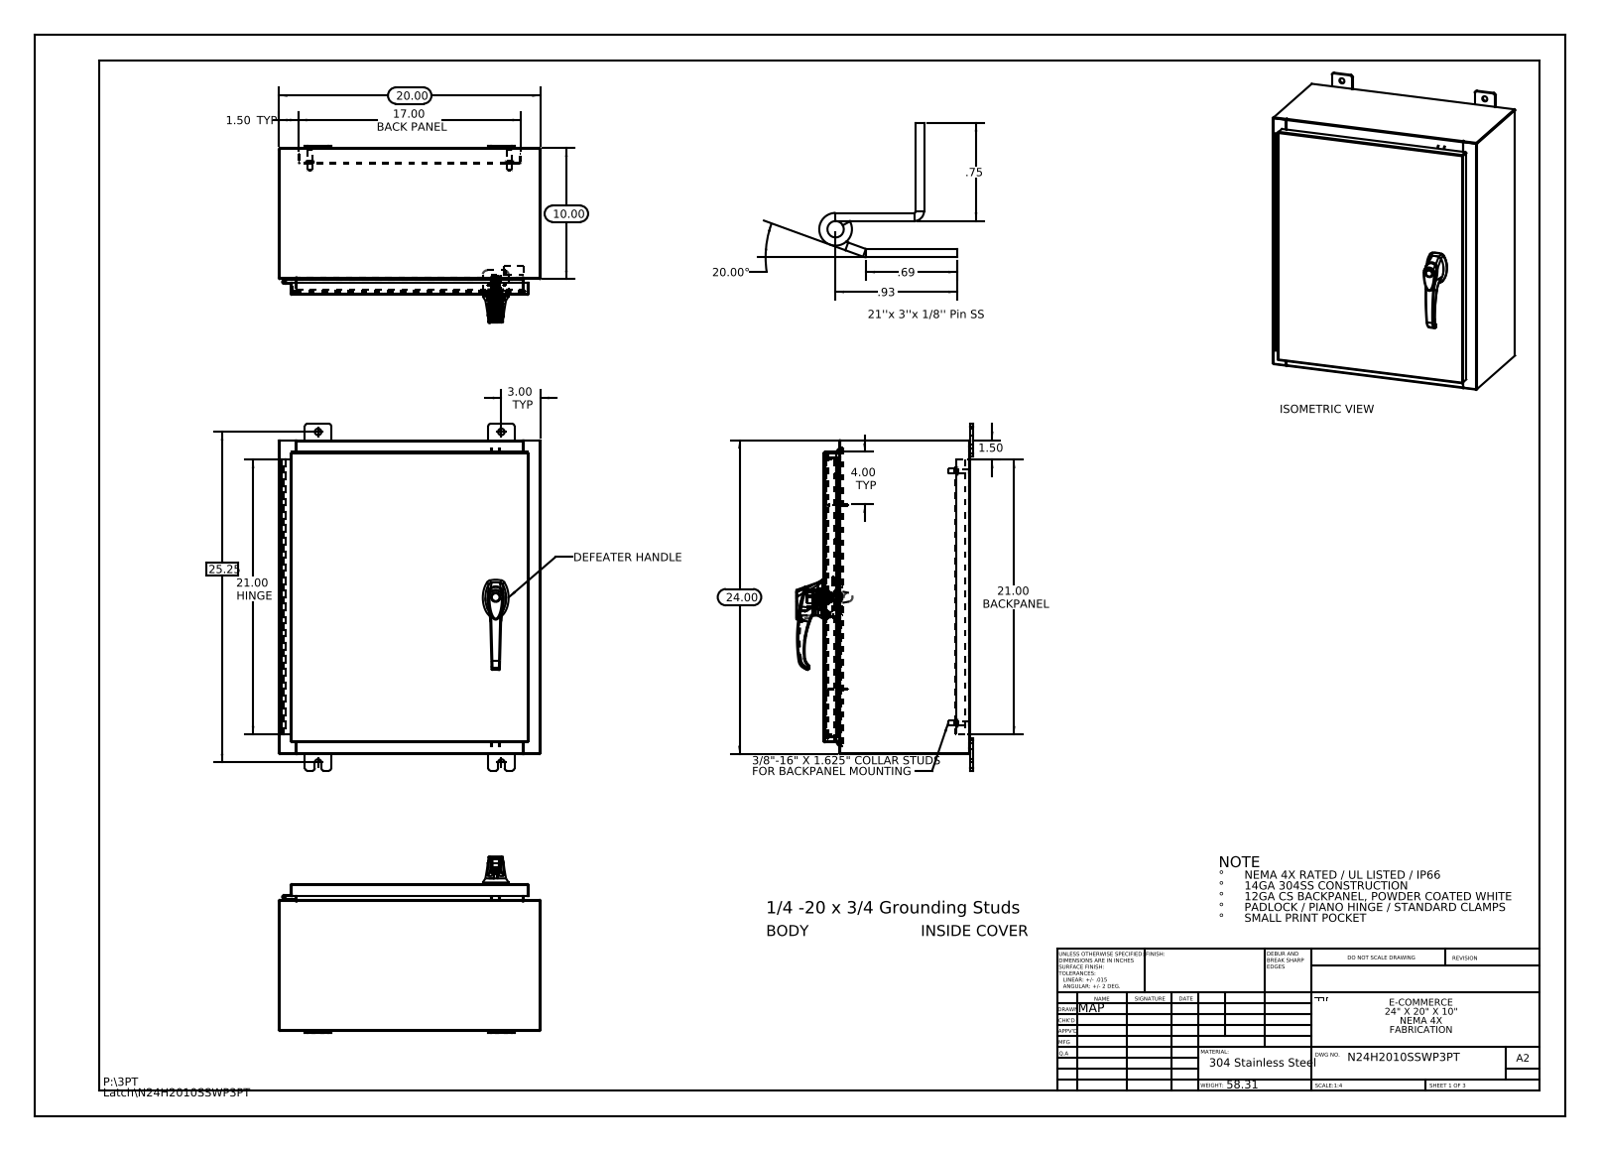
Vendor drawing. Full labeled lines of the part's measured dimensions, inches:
Part name (STEP PRODUCT): N24H2010SSWP3PT Defeater Handle - 3 - 2500-51 ZN; g26103103_26163303; N24H2010SSWP3PT Cover; 033060_032151 (+8 more)
STEP written by: SolidWorks 2013 (CONFIG_CONTROL_DESIGN)
Units: inches
Bodies: 31 solids, 2412 faces (865 planar, 893 cylindrical, 654 other)
Overall size (bounding box): 26.5 × 20 × 13.495
Volume: 207.2 in³ · Surface area: 5 153 in²
Round holes (diameter × count): ⌀0.5 ×8, ⌀0.25 ×4, ⌀0.138 ×3, ⌀0.161 ×3, ⌀0.079 ×2, ⌀0.203 ×2, ⌀0.313 ×2, ⌀0.437 ×2, ⌀0.125 ×1, ⌀0.125 ×1, ⌀0.197 ×1, ⌀0.276 ×1
Round bosses / shafts (diameter × count): ⌀0.625 ×4, ⌀0.375 ×4, ⌀0.33 ×4, ⌀1.181 ×1, ⌀0.748 ×1, ⌀0.68 ×1, ⌀0.661 ×1, ⌀0.639 ×1
Partial cylindrical surfaces — rounded edges, fillets, slot ends (radius × count): R0.118 ×37, R0.006 ×33, R0.19 ×24, R0.013 ×22, R0.088 ×18, R0.039 ×15, R0.028 ×12, R0.008 ×6
Main face-to-face distances: 0.075, 11.126, 19.925, 11.051, 11.201, 23.925, 0.104, 1, 1.075, 10.051
Hole centre spacings: 7.68, 0.295, 0.625, 0.841, 1.25, 1.313, 1.561, 1.858
